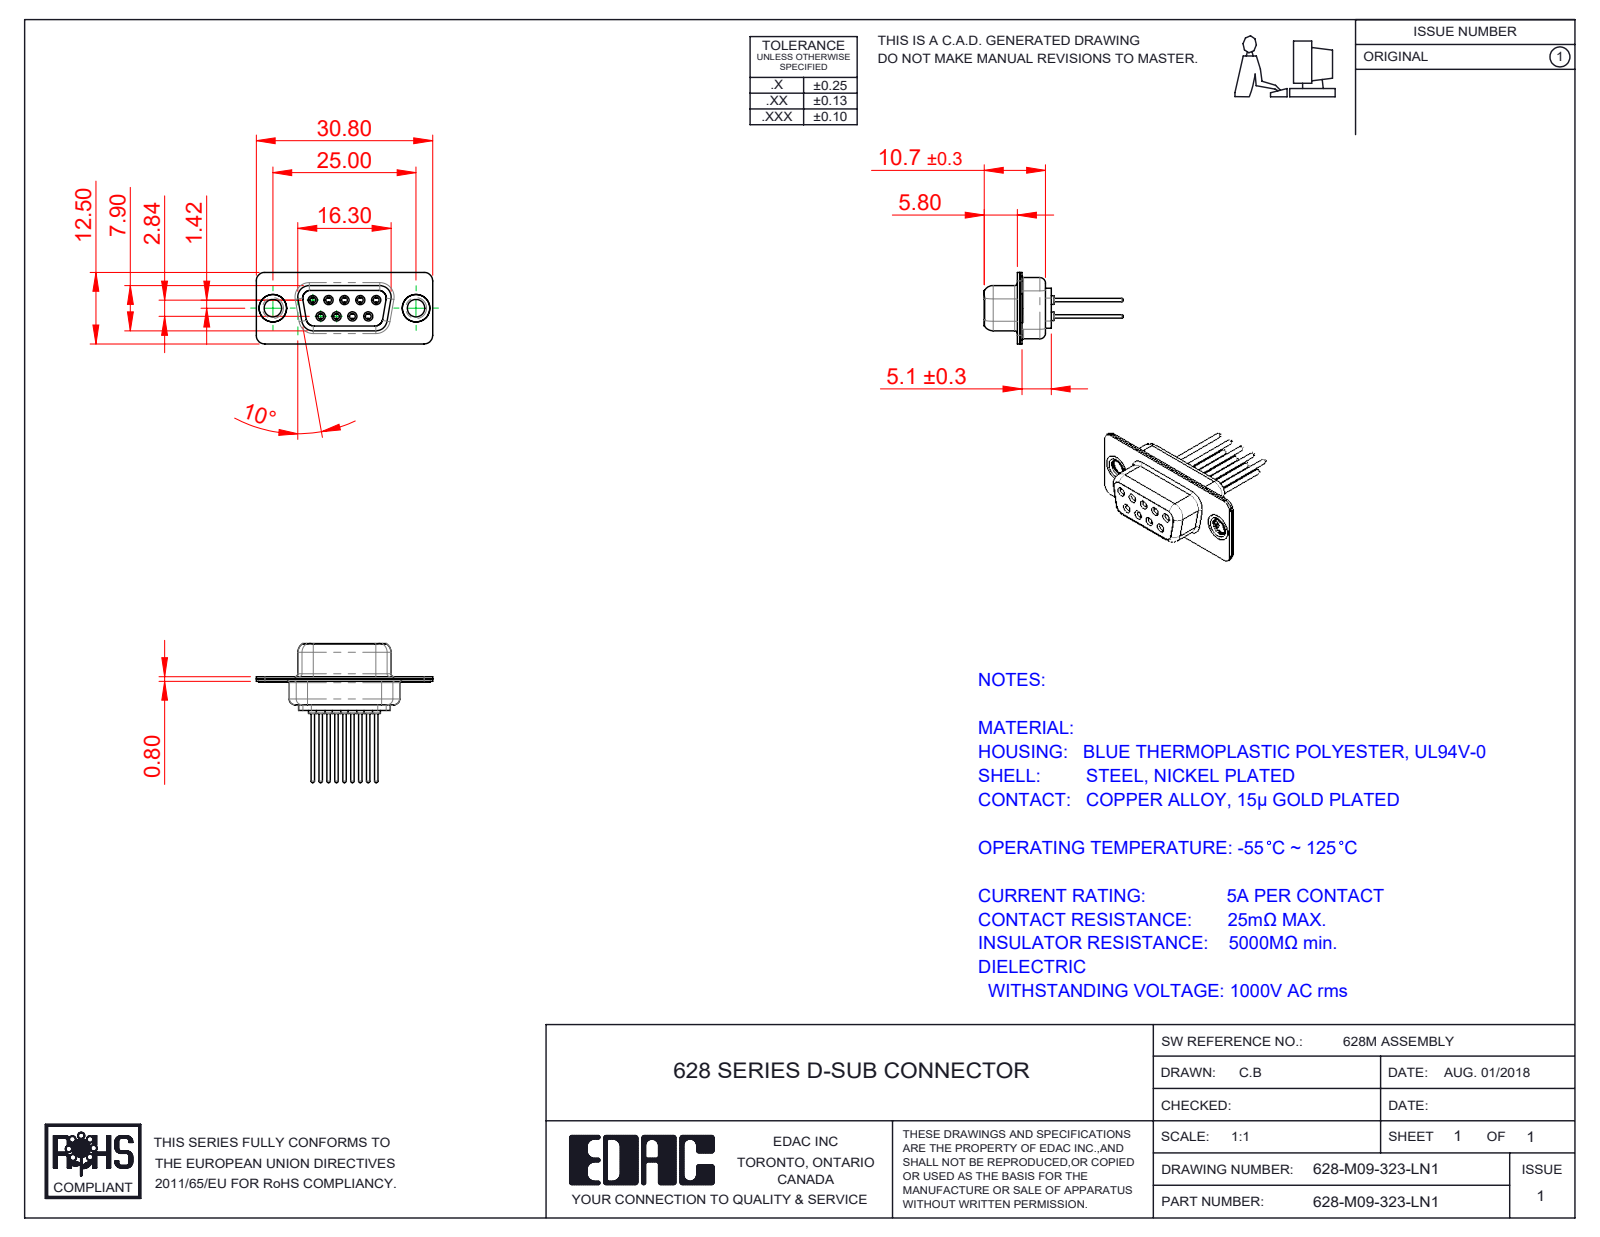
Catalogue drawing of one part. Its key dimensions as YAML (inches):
part_name: "628M Shell Front_09 Contacts; 628M Contact Row 2_23; 628-M09-323-LN1; 628M Thru Hole Rivet (+3 more)"
step_written_by: "SolidWorks 2020 (CONFIG_CONTROL_DESIGN)"
units: inches
bodies: {solids: 14, faces: 748, planar: 202, cylindrical: 292, other: 254}
overall_size: [1.213, 0.956, 0.492]
volume: 0.1
surface_area: 6.805
round_holes:
  - {diameter: 0.039, count: 9}
  - {diameter: 0.043, count: 9}
  - {diameter: 0.067, count: 9}
  - {diameter: 0.071, count: 9}
  - {diameter: 0.079, count: 9}
  - {diameter: 0.12, count: 2}
  - {diameter: 0.157, count: 2}
  - {diameter: 0.189, count: 2}
round_bosses_or_shafts:
  - {diameter: 0.087, count: 9}
  - {diameter: 0.063, count: 9}
  - {diameter: 0.059, count: 9}
  - {diameter: 0.024, count: 9}
  - {diameter: 0.197, count: 2}
  - {diameter: 0.193, count: 2}
  - {diameter: 0.14, count: 2}
partial_cylinders:
  - {radius: 0.059, count: 16}
  - {radius: 0.079, count: 12}
  - {radius: 0.053, count: 8}
  - {radius: 0.063, count: 8}
  - {radius: 0.01, count: 4}
  - {radius: 0.02, count: 4}
  - {radius: 0.024, count: 4}
  - {radius: 0.026, count: 4}
face_to_face_distances: [0.016, 0.055, 0.018, 0.333, 0.031, 0.35, 0.071, 0.039, 0.244, 0.053]
hole_center_spacings: [0.124, 0.109, 0.218, 0.198, 0.198, 0.327, 0.28, 0.294]
